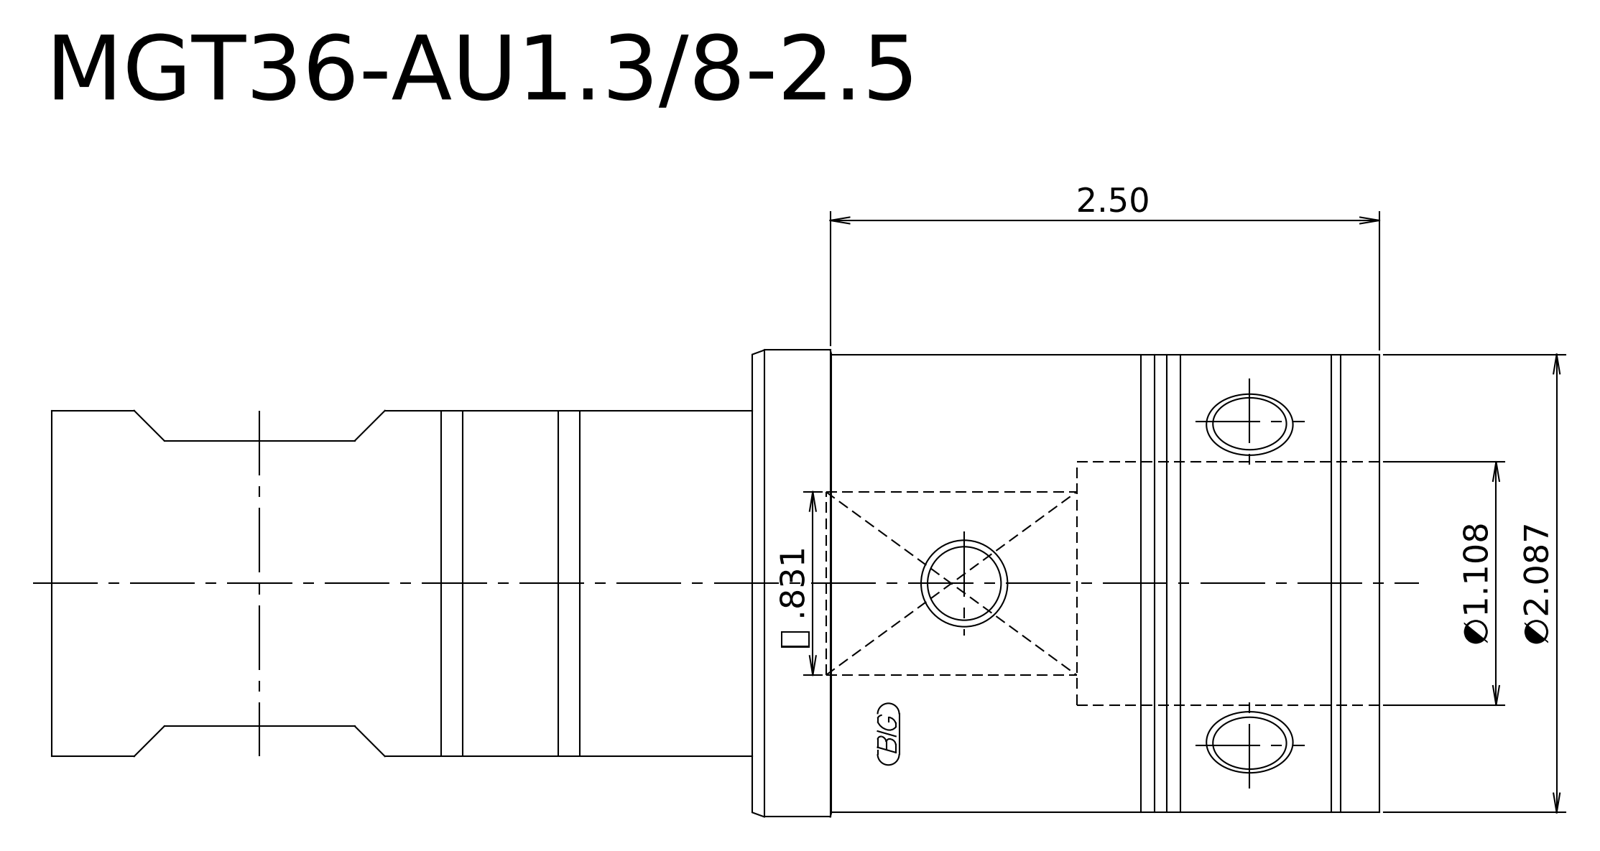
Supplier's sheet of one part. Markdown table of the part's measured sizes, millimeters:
| quantity | value |
| --- | --- |
| STEP written by | Kubotek KeyCreator 2011 V10.0.2 (22737) (automotive_design) |
| units | millimeters |
| bodies | 1 solid, 8 faces (3 planar, 3 cylindrical, 2 other) |
| overall size | 153.5 × 54 × 54 |
| volume | 262 440 mm³ |
| surface area | 26 768 mm² |
| round bosses / shafts (diameter × count) | 54 × 1, 53 × 1, 40 × 1 |
| main face-to-face distances | 153.5, 72.5, 81 |
